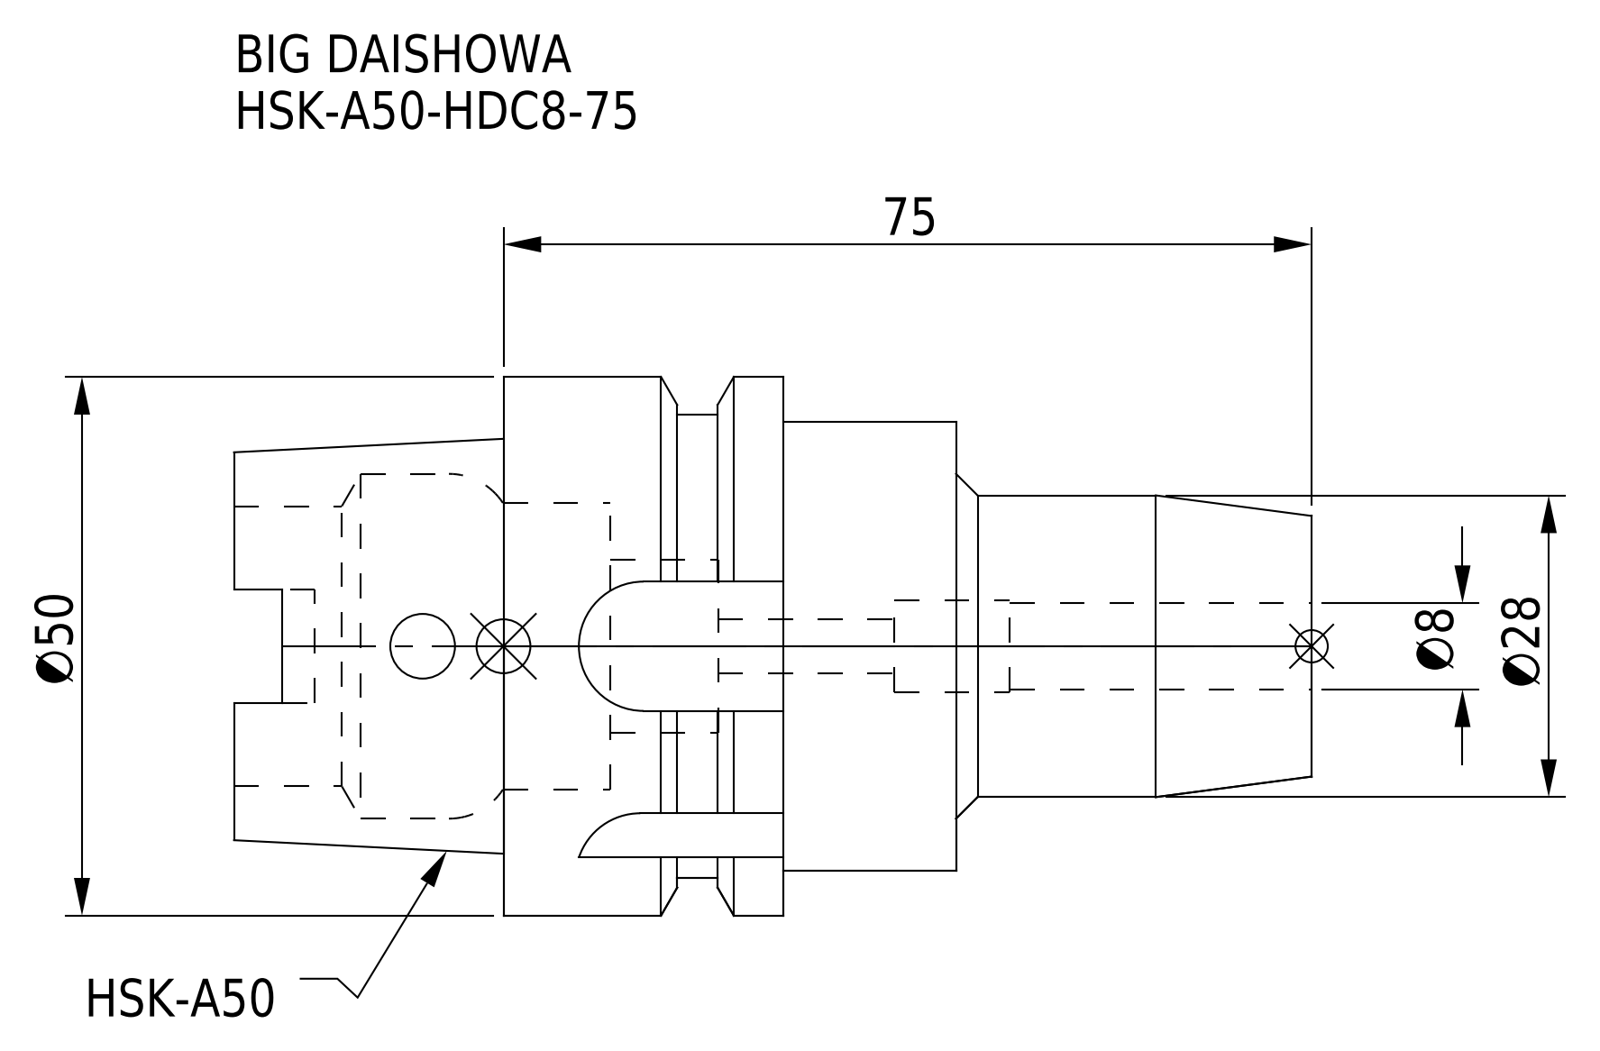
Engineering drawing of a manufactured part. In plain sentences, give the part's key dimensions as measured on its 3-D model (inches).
The part is named "HSK-A50-HDC8-75". Its 3-D file was written by "CREO PARAMETRIC BY PTC INC, 2016380 (AUTOMOTIVE_DESIGN)". It is 1 solid with 96 faces: 39 planar, 39 cylindrical and 18 other. Overall it measures 3.937 by 1.969 by 1.969 inches. Its volume is 5.369 cubic inches and its surface area 32.5 square inches. Round holes: 1 of diameter 0.197, 1 of diameter 0.236, 1 of diameter 0.315, 1 of diameter 0.335, 1 of diameter 0.63, 1 of diameter 1.024, 1 of diameter 1.047, 1 of diameter 1.26. Round bosses or shafts: 1 of diameter 1.969, 1 of diameter 1.693, 1 of diameter 1.638, 1 of diameter 1.102. Partial cylindrical surfaces (rounded edges, fillets, slot ends): 4 of radius 0.094, 4 of radius 0.236. The main face-to-face distances are 1.654, 0.63, 1.024, 1.299, 1.929, 2.953, 2.561, 1.262, 0.632, 0.392.
